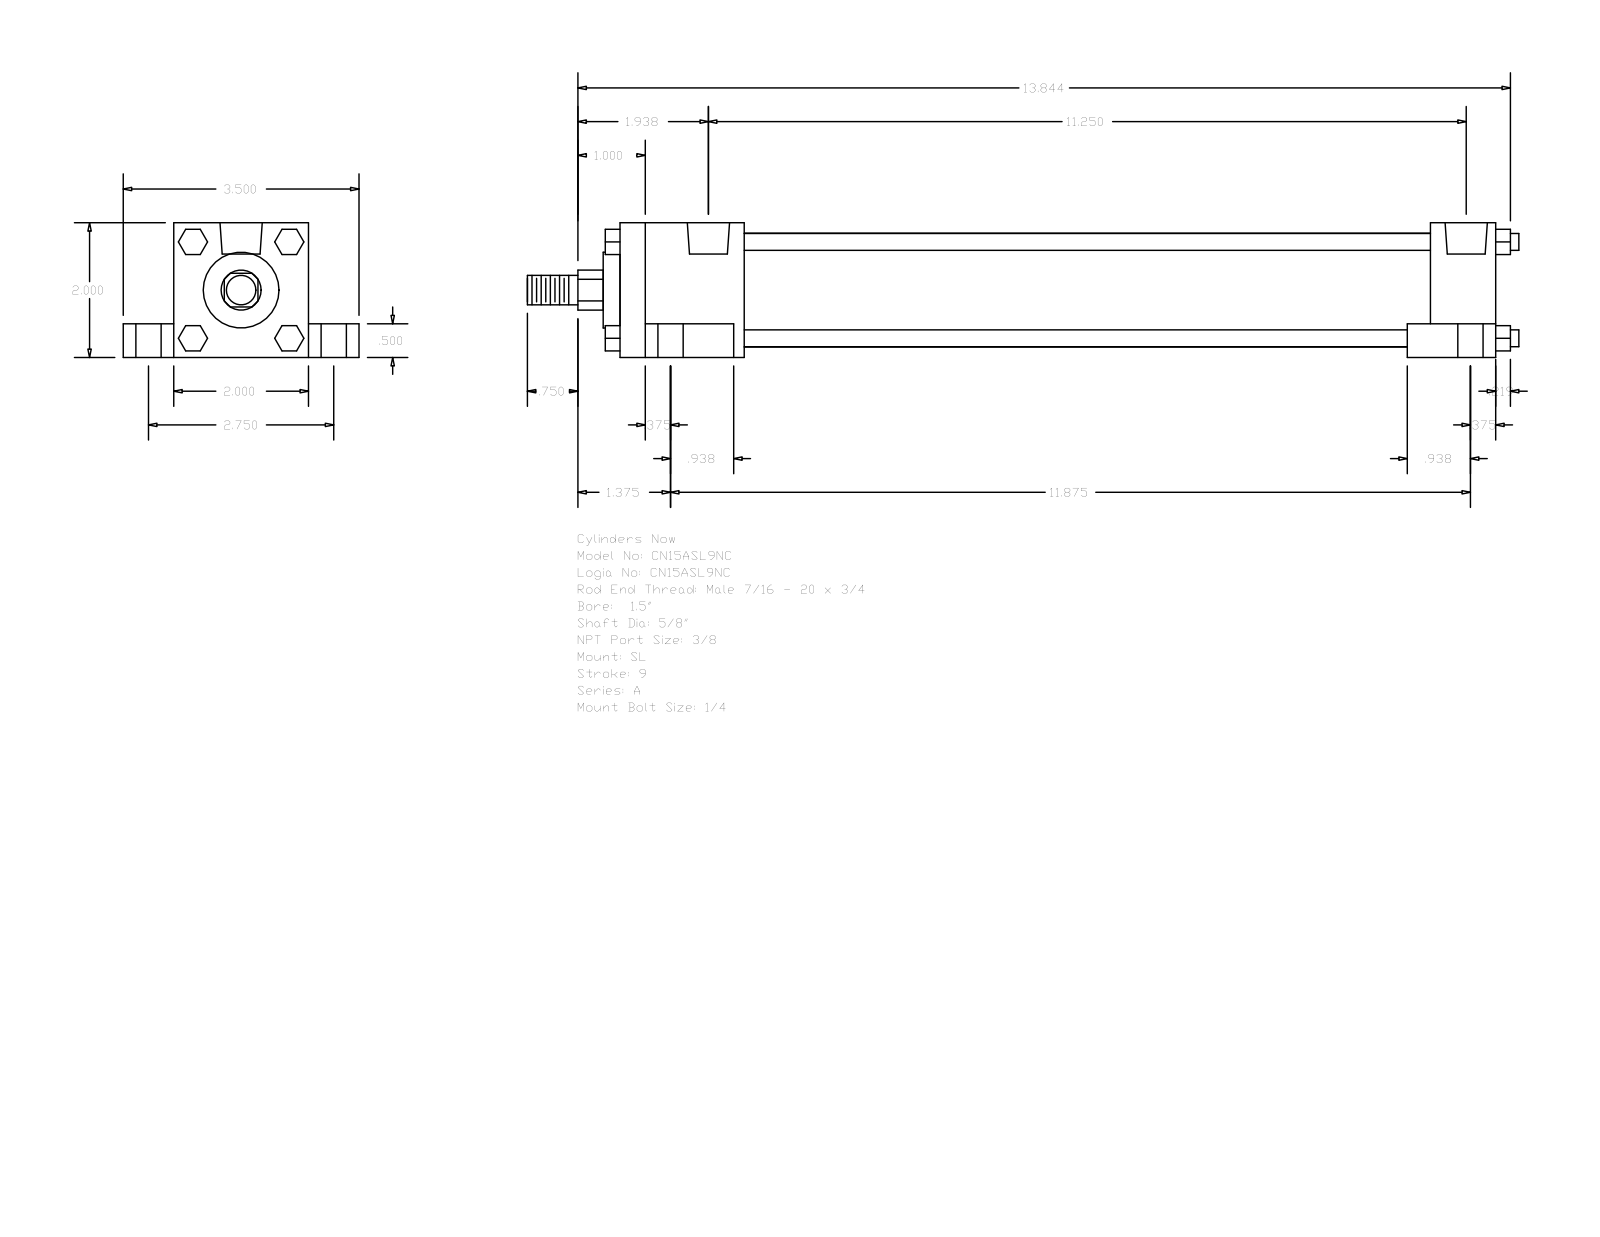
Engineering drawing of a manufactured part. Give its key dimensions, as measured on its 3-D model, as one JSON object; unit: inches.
{"part_name": "A_SL__0150_0.625", "step_written_by": "GSSL Pune (CONFIG_CONTROL_DESIGN)", "units": "inches", "bodies": {"solids": 0, "faces": 148, "planar": 112, "cylindrical": 36, "other": 0}, "overall_size": [14.719, 3.5, 2], "round_holes": [[0.219, 4], [0.375, 4], [0.625, 4], [0.627, 2]], "round_bosses_or_shafts": [[0.25, 4], [1.69, 1], [1.125, 1], [0.625, 1], [0.437, 1]], "partial_cylinders_radius": [[0.297, 1]], "face_to_face_distances": [2, 0.75, 1.5, 0.5, 2.75, 13, 0.375, 12.031, 0.969, 1.844], "hole_center_spacings": [0.156, 1.376, 1.392, 1.485, 1.552, 2.75, 10.937, 11.094]}
